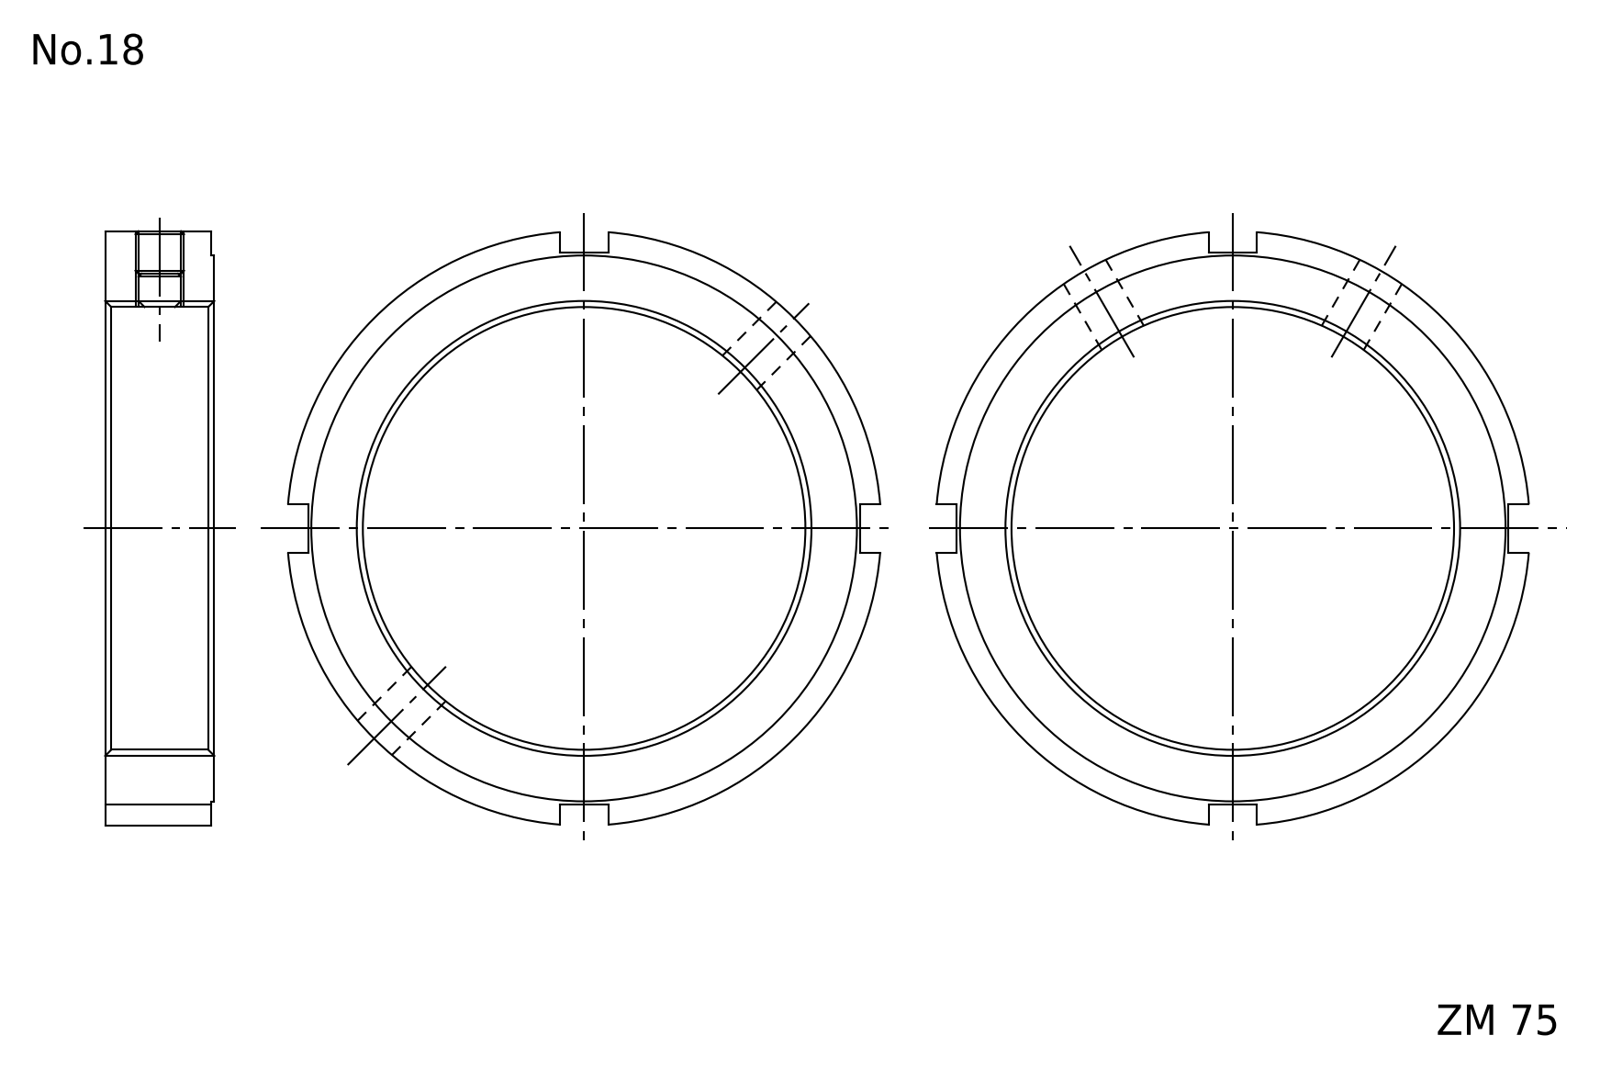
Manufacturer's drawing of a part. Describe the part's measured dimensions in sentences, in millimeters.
The part is named "FKD ZM 75". Its 3-D file was written by "Autodesk Inventor 2011 (AUTOMOTIVE_DESIGN)". It is 1 solid with 23 faces: 15 planar, 8 cylindrical and 0 other. Overall it measures 97.67 by 97.67 by 18 millimeters. Its volume is 52 933 cubic millimeters and its surface area 16 609 square millimeters. Round holes: 2 of diameter 6.65, 1 of diameter 75. Round bosses or shafts: 1 of diameter 98, 1 of diameter 90. The main face-to-face distances are 18, 0.5, 17.5, 41.5, 49.5, 91, 8.
